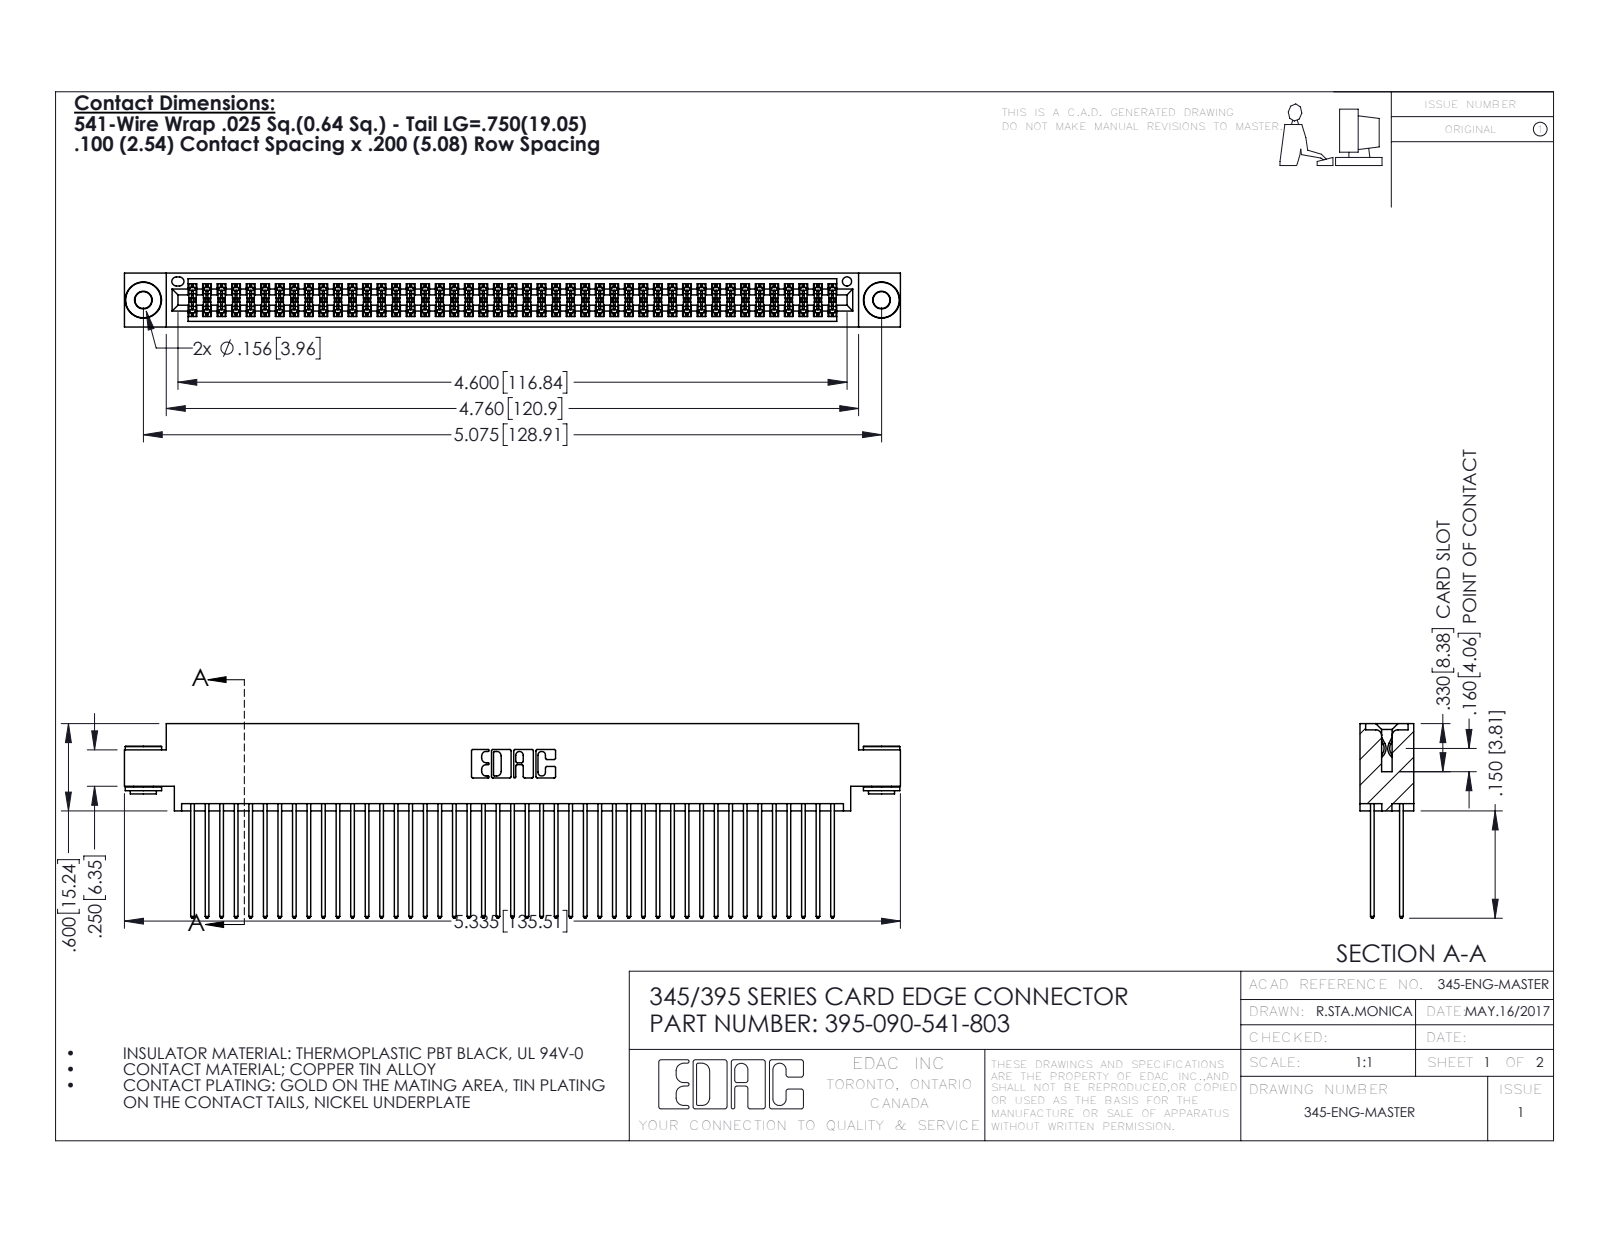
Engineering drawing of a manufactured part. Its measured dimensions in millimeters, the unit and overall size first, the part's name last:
Units: millimetres
Overall size (bounding box): 135.5 × 34 × 9.4
Round holes (diameter × count): ⌀2.9 ×2, ⌀4 ×2, ⌀1.6 ×1
Round bosses / shafts (diameter × count): ⌀6.4 ×2, ⌀4.6 ×2, ⌀3.5 ×2
Partial cylindrical surfaces — rounded edges, fillets, slot ends (radius × count): R0.2 ×135, R0.3 ×90, R0.3 ×22, R0.2 ×6, R0.8 ×6, R0.7 ×3, R0.4 ×2, R0.5 ×2
Main face-to-face distances: 1.8, 7.6, 5.1, 2.5, 6.9, 0.6, 9.4, 5.7, 4.4, 3.8
Hole centre spacings: 6.9, 122.9, 128.9
Volume: 13 600 mm³ · Surface area: 22 950 mm²
Bodies: 93 solids, 4668 faces (3064 planar, 1596 cylindrical, 8 other)
Part name (STEP PRODUCT): 345-250-002_345-250-002-102; 345 Part_0.170 Offset - 0.156 Dia-TH; 395-090-541-803; 345-292-001_345-293-141
STEP written by: SolidWorks 2016 (CONFIG_CONTROL_DESIGN)
